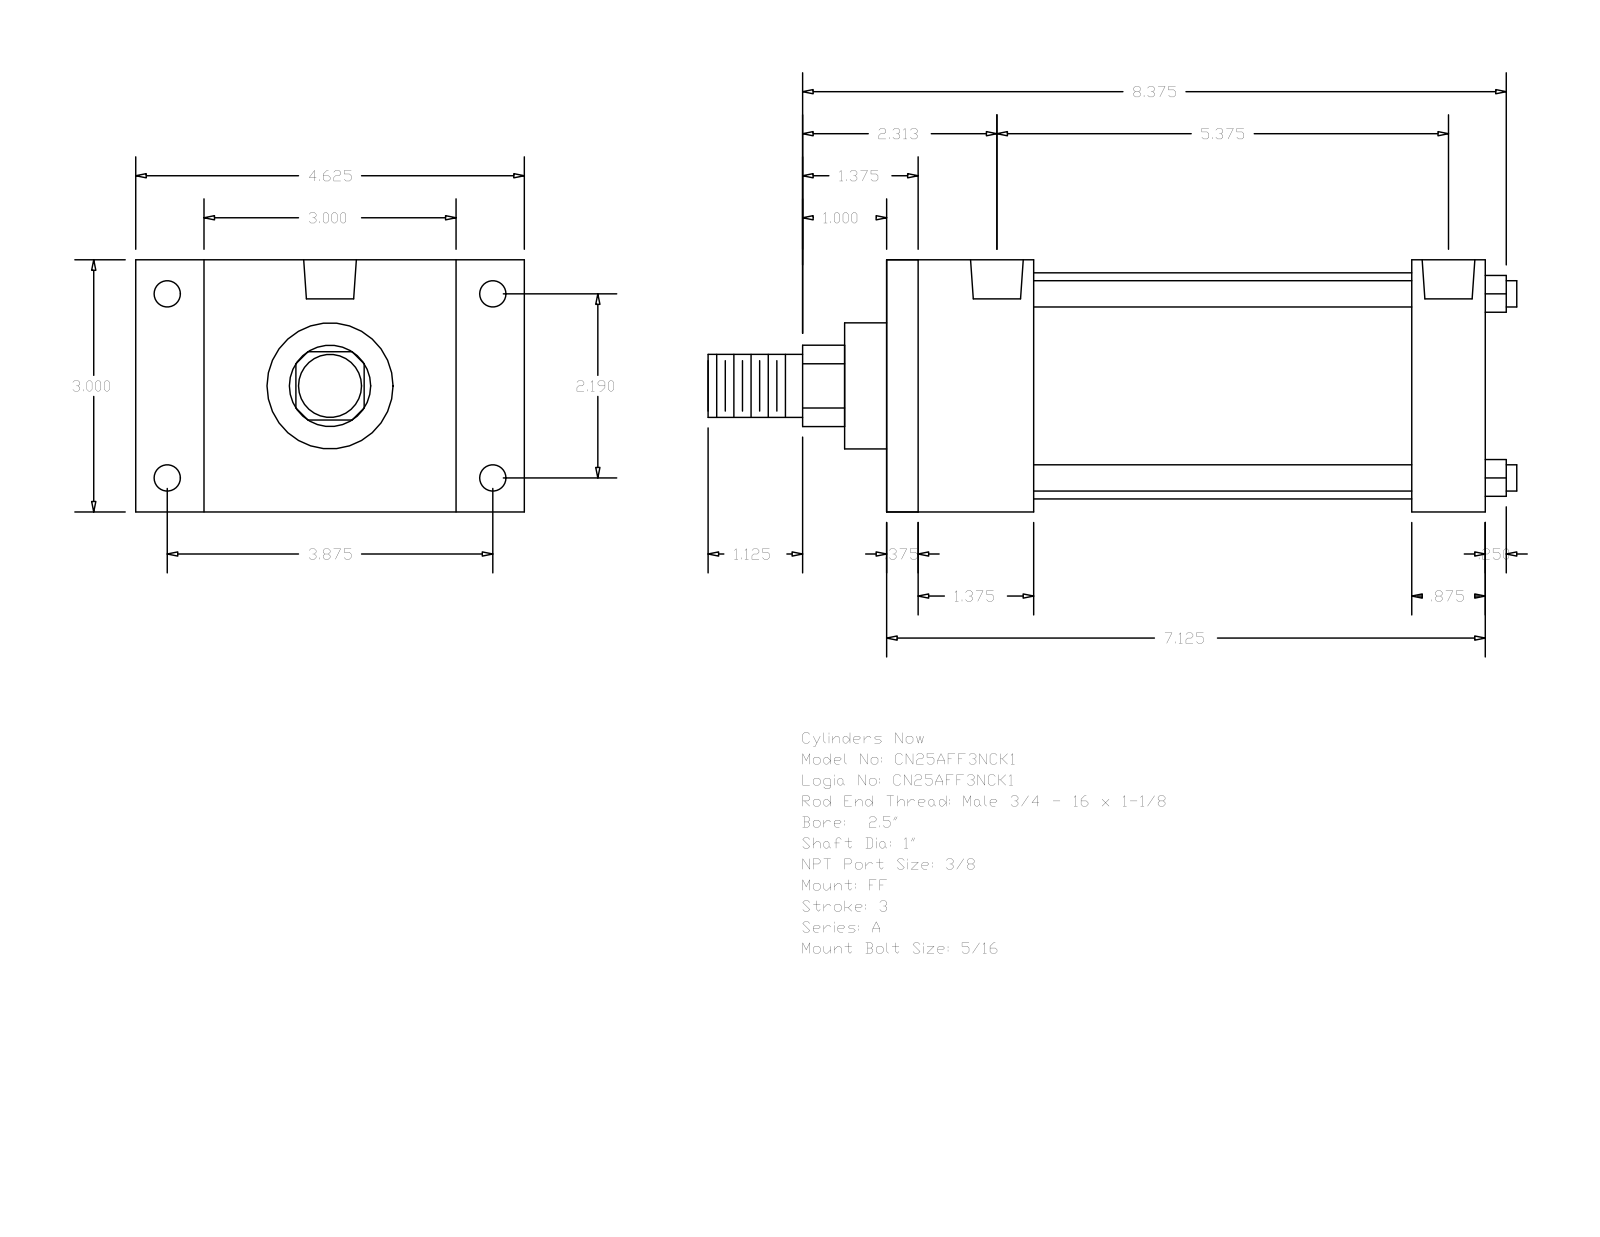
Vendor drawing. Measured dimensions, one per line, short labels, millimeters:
name: A_FF__0250_1
written by: GSSL Pune (CONFIG_CONTROL_DESIGN)
unit: mm
bodies: 0 solids, 92 faces (64 planar, 28 cylindrical, 0 other)
size: 244.47 × 117.47 × 76.2
holes: 4× ⌀5.56, 4× ⌀7.94, 2× ⌀15.93
bosses: 4× ⌀7.94, 1× ⌀68.33, 1× ⌀38.1, 1× ⌀25.4, 1× ⌀19.05
rounds: 1× R12.29
face distances: 76.2, 180.98, 9.52, 171.46, 44.45, 158.75, 34.93, 149.23, 114.3, 136.53
hole spacings: 2.38, 55.62, 98.42, 113.05, 138.9, 141.28, 136.52
